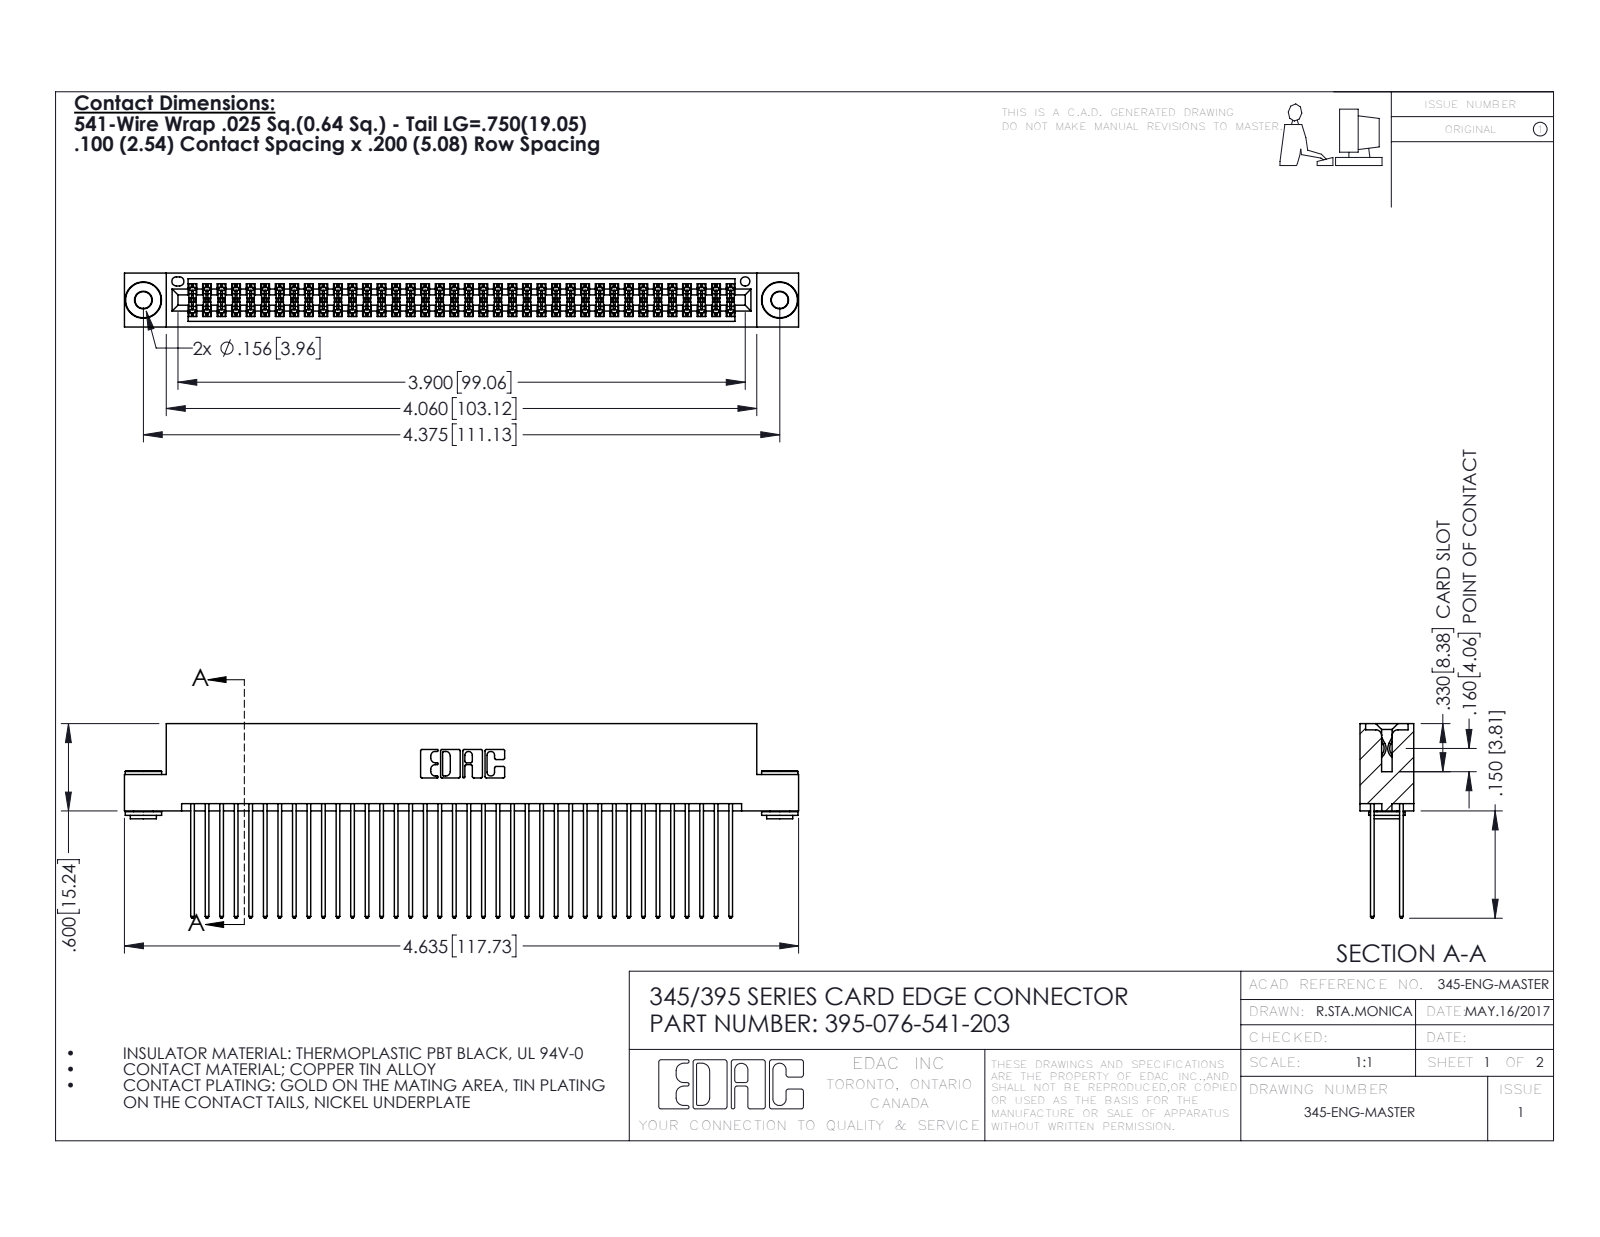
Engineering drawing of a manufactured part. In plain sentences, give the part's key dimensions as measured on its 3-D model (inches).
The part is named "345-292-001_345-293-141; 345-250-002_345-250-002-102; 345 Part_Flush Mounting Lugs - 0.156 Dia-TH; 395-076-541-203". Its 3-D file was written by "SolidWorks 2016 (CONFIG_CONTROL_DESIGN)". It is 79 solids with 3964 faces: 2598 planar, 1358 cylindrical and 8 other. Overall it measures 4.635 by 1.337 by 0.37 inches. Its volume is 0.723 cubic inches and its surface area 30.54 square inches. Round holes: 2 of diameter 0.116, 2 of diameter 0.156, 1 of diameter 0.064. Round bosses or shafts: 2 of diameter 0.25, 2 of diameter 0.18, 2 of diameter 0.136. Partial cylindrical surfaces (rounded edges, fillets, slot ends): 114 of radius 0.006, 76 of radius 0.01, 22 of radius 0.01, 6 of radius 0.007, 6 of radius 0.031, 3 of radius 0.026, 2 of radius 0.014, 2 of radius 0.019. The main face-to-face distances are 0.072, 0.298, 0.2, 0.025, 0.098, 0.272, 0.225, 0.37, 0.175, 0.149. The hole center spacings are 0.27, 4.139, 4.375.
